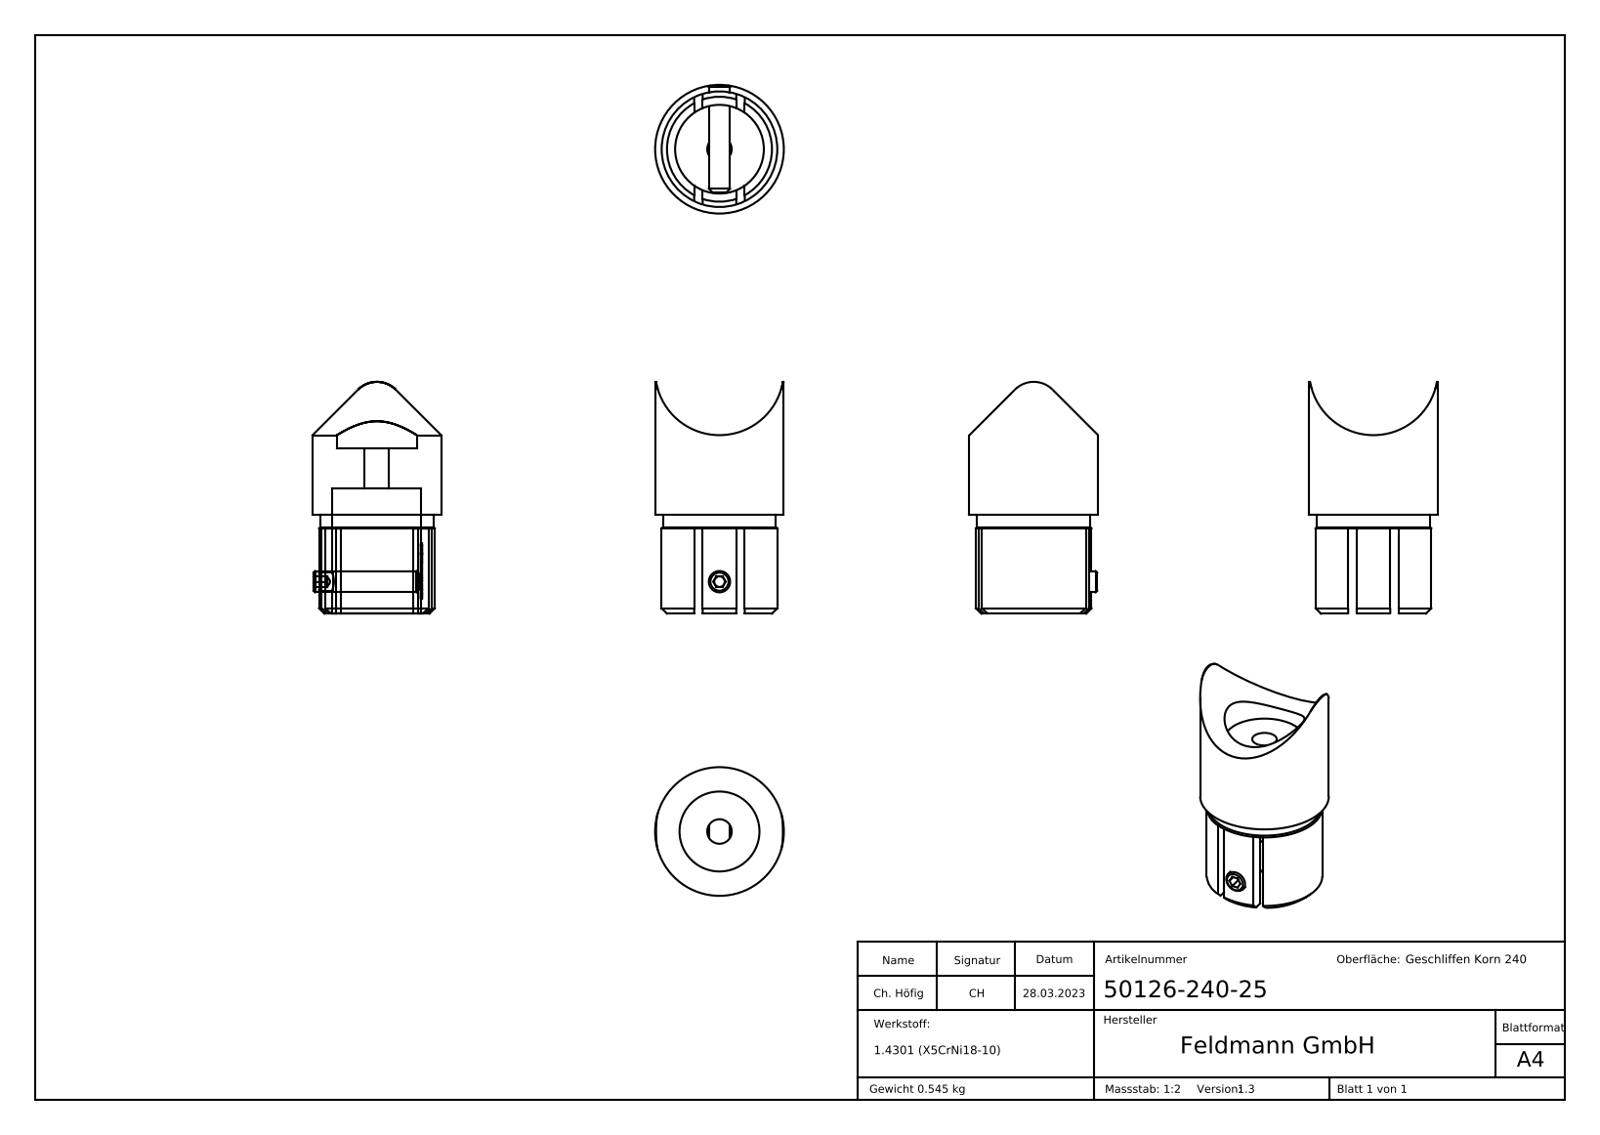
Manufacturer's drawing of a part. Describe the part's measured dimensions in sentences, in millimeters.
The part is named "DIN913_DIN 913 M8x40; 5012X-240 Teil1_50126-240-25 Teil1; 50126-240-25". Its 3-D file was written by "SolidWorks 2018 (CONFIG_CONTROL_DESIGN)". It is 2 solids with 311 faces: 147 planar, 47 cylindrical and 117 other. Overall it measures 87.01 by 48.3 by 48.3 millimeters. Its volume is 68 948 cubic millimeters and its surface area 22 531 square millimeters. Round holes: 1 of diameter 6.8, 1 of diameter 9.2, 1 of diameter 30, 1 of diameter 33.3. Round bosses or shafts: 1 of diameter 48.3, 1 of diameter 43.4, 1 of diameter 42.4, 1 of diameter 8. Partial cylindrical surfaces (rounded edges, fillets, slot ends): 1 of radius 10, 1 of radius 16.75, 1 of radius 24.15. The main face-to-face distances are 15, 3.2, 15.8, 10, 25, 19, 12.6, 37, 47, 62.
